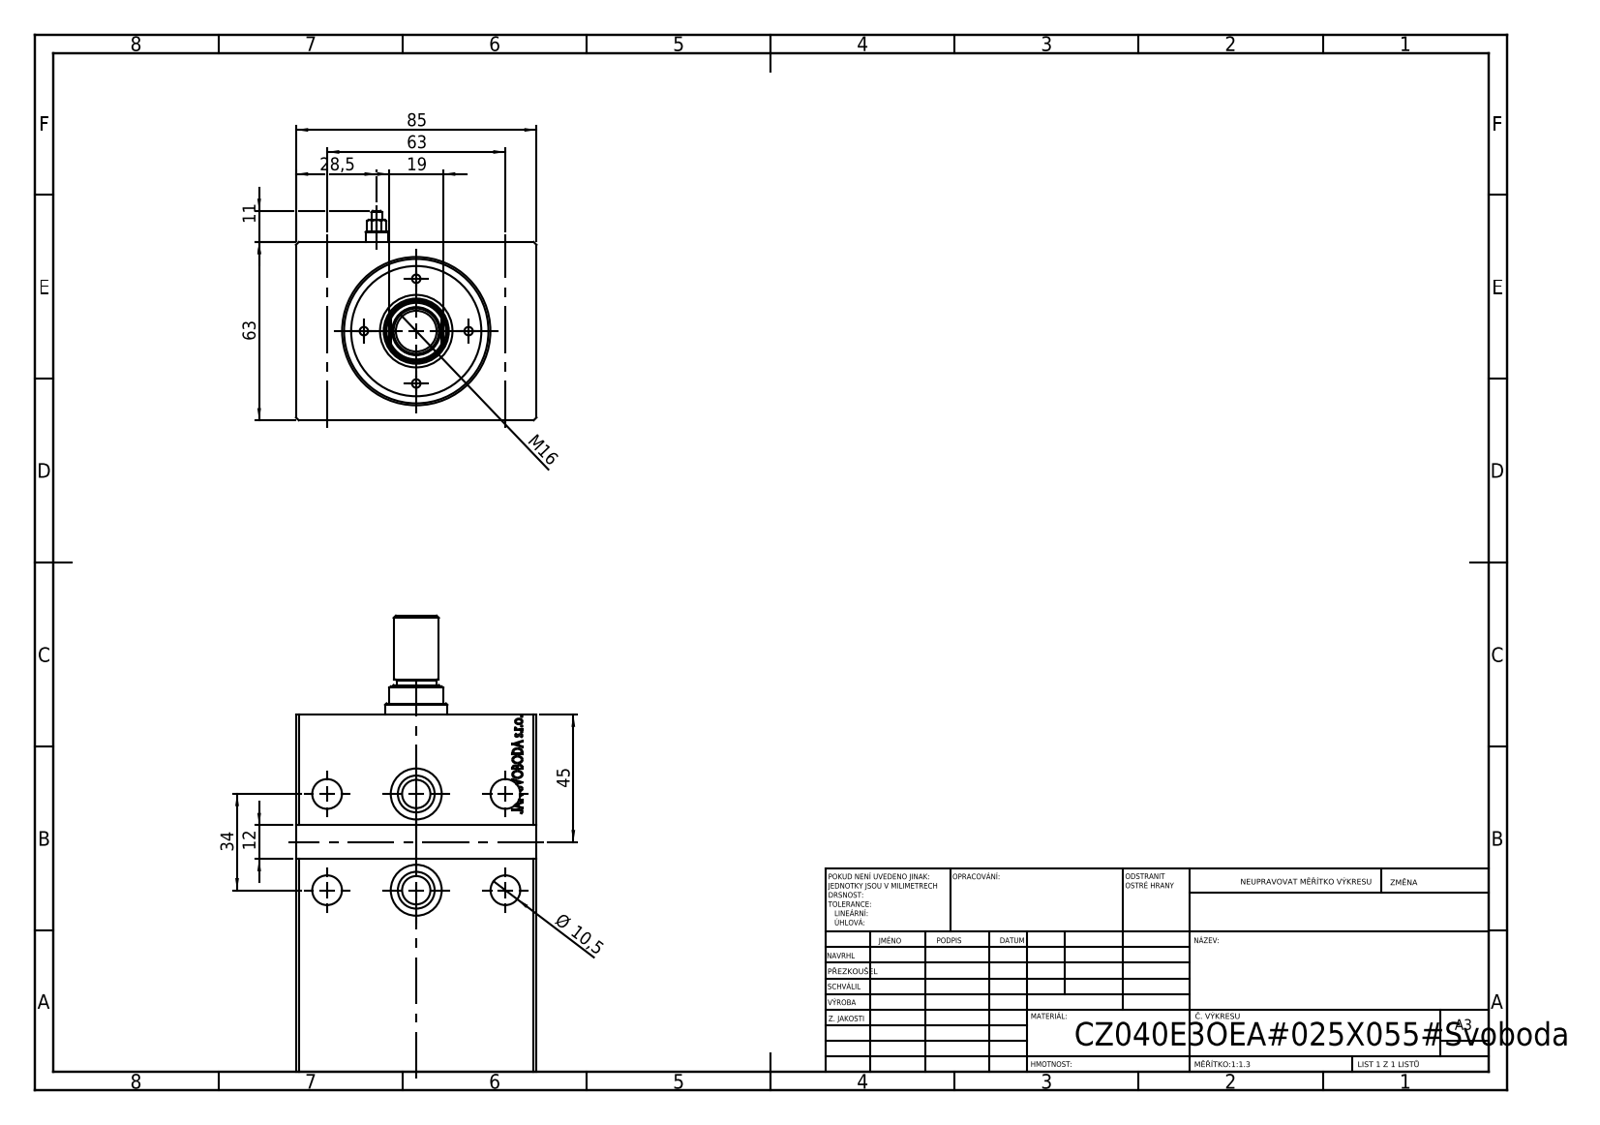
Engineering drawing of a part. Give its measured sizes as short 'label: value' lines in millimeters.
written by: SolidWorks 2019 (CONFIG_CONTROL_DESIGN)
unit: mm
bodies: 1 solid, 779 faces (383 planar, 30 cylindrical, 366 other)
size: 126 × 85 × 63
volume: 502 248 mm³; area: 70 581 mm²
holes: 4× ⌀10.5, 2× ⌀8, 2× ⌀10, 2× ⌀18, 1× ⌀36, 1× ⌀40, 1× ⌀51
bosses: 2× ⌀13
face distances: 63, 85, 126, 110.7, 15.3, 2, 61, 125.8, 15.1, 10
hole spacings: 31.5, 46.35, 34, 63, 71.59, 15.65, 18.85, 30.41
